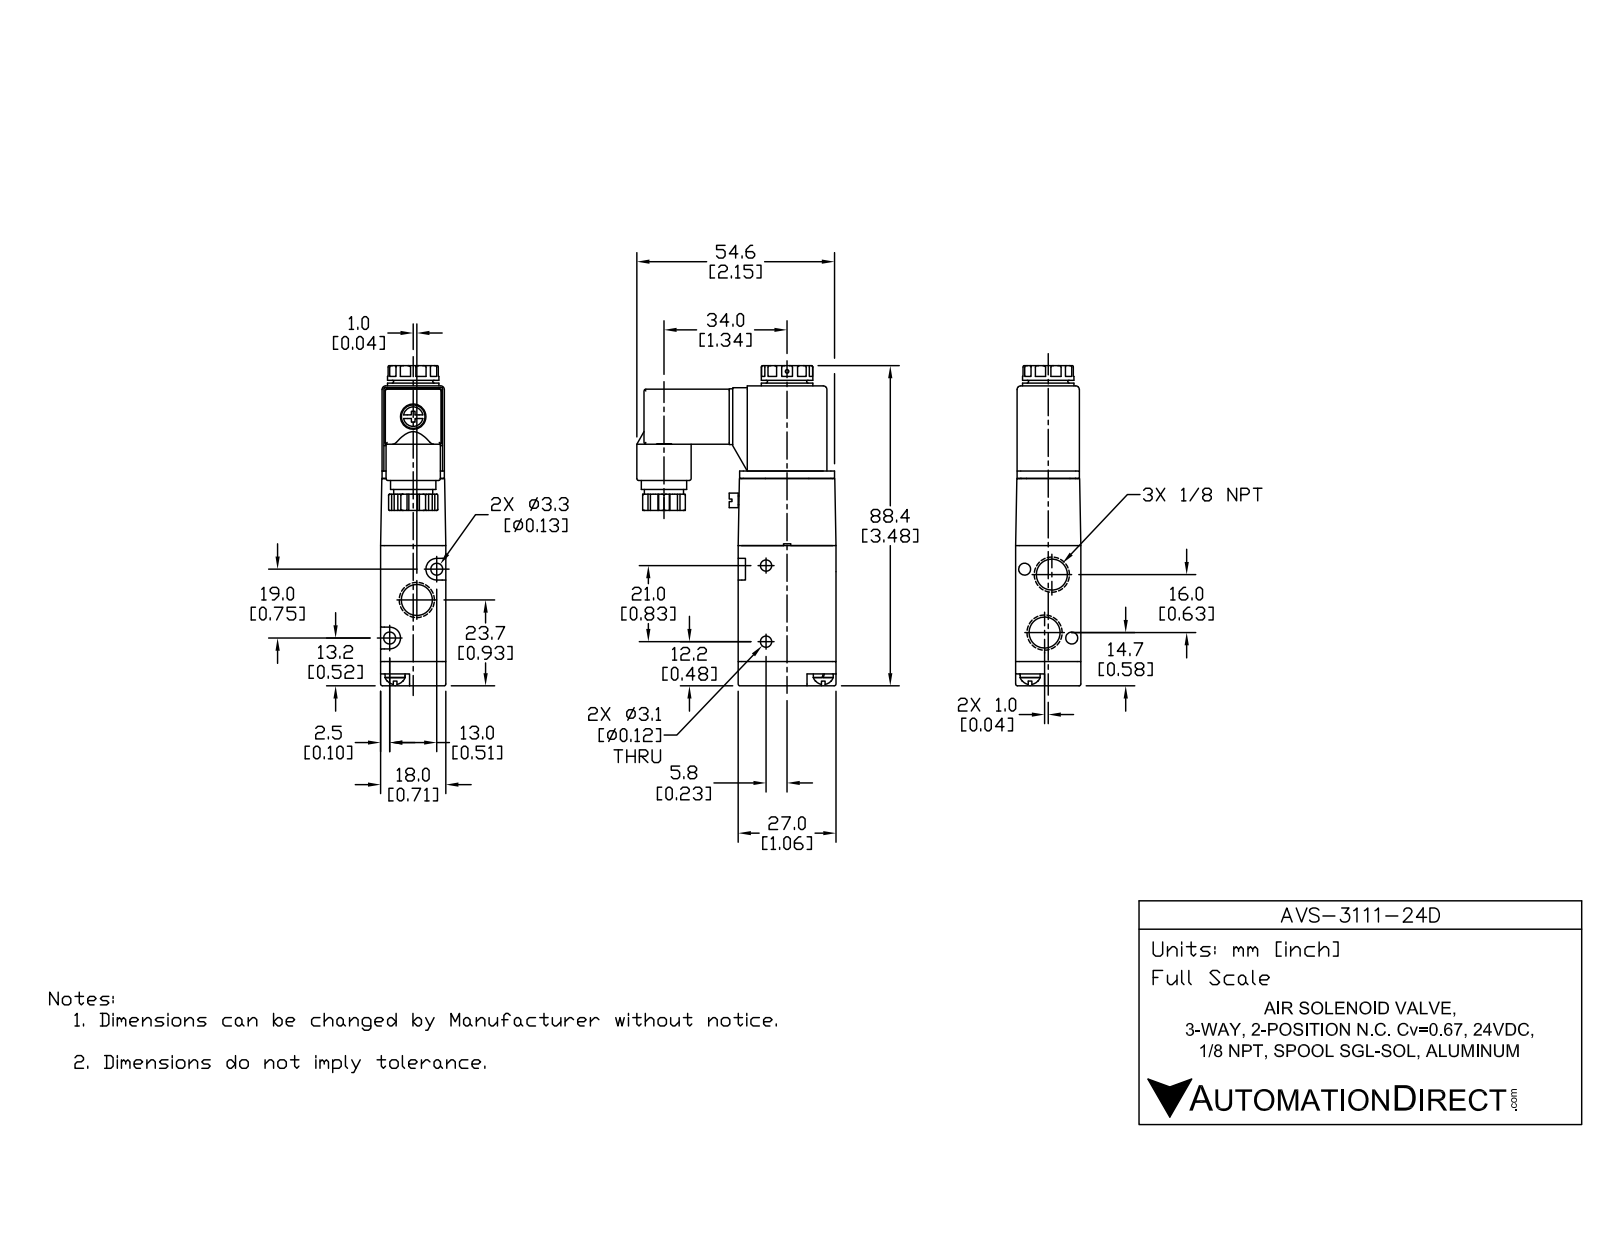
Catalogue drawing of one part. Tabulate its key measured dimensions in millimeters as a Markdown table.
| quantity | value |
| --- | --- |
| part name | AVS-3111-24D |
| STEP written by | SolidWorks 2015 (CONFIG_CONTROL_DESIGN) |
| units | millimeters |
| bodies | 4 solids, 137 faces (72 planar, 51 cylindrical, 14 other) |
| overall size | 88.4 × 55 × 18 |
| volume | 44 253 mm³ |
| surface area | 15 257 mm² |
| round holes (diameter × count) | 3.3 × 4, 8.43 × 3, 9.3 × 1 |
| round bosses / shafts (diameter × count) | 15 × 1, 14.4 × 1, 12.6 × 1, 10.8 × 1, 9 × 1, 6.8 × 1 |
| partial cylindrical surfaces (radius × count) | 0.5 × 15, 1 × 4, 3 × 2 |
| main face-to-face distances | 32, 18, 16.7, 1.3, 2.31, 6.7, 38.7, 81.9, 75.2, 43.2 |
| hole center spacings | 7.65, 18.34, 7.28, 9, 10.12, 12.9, 16.12, 21 |
